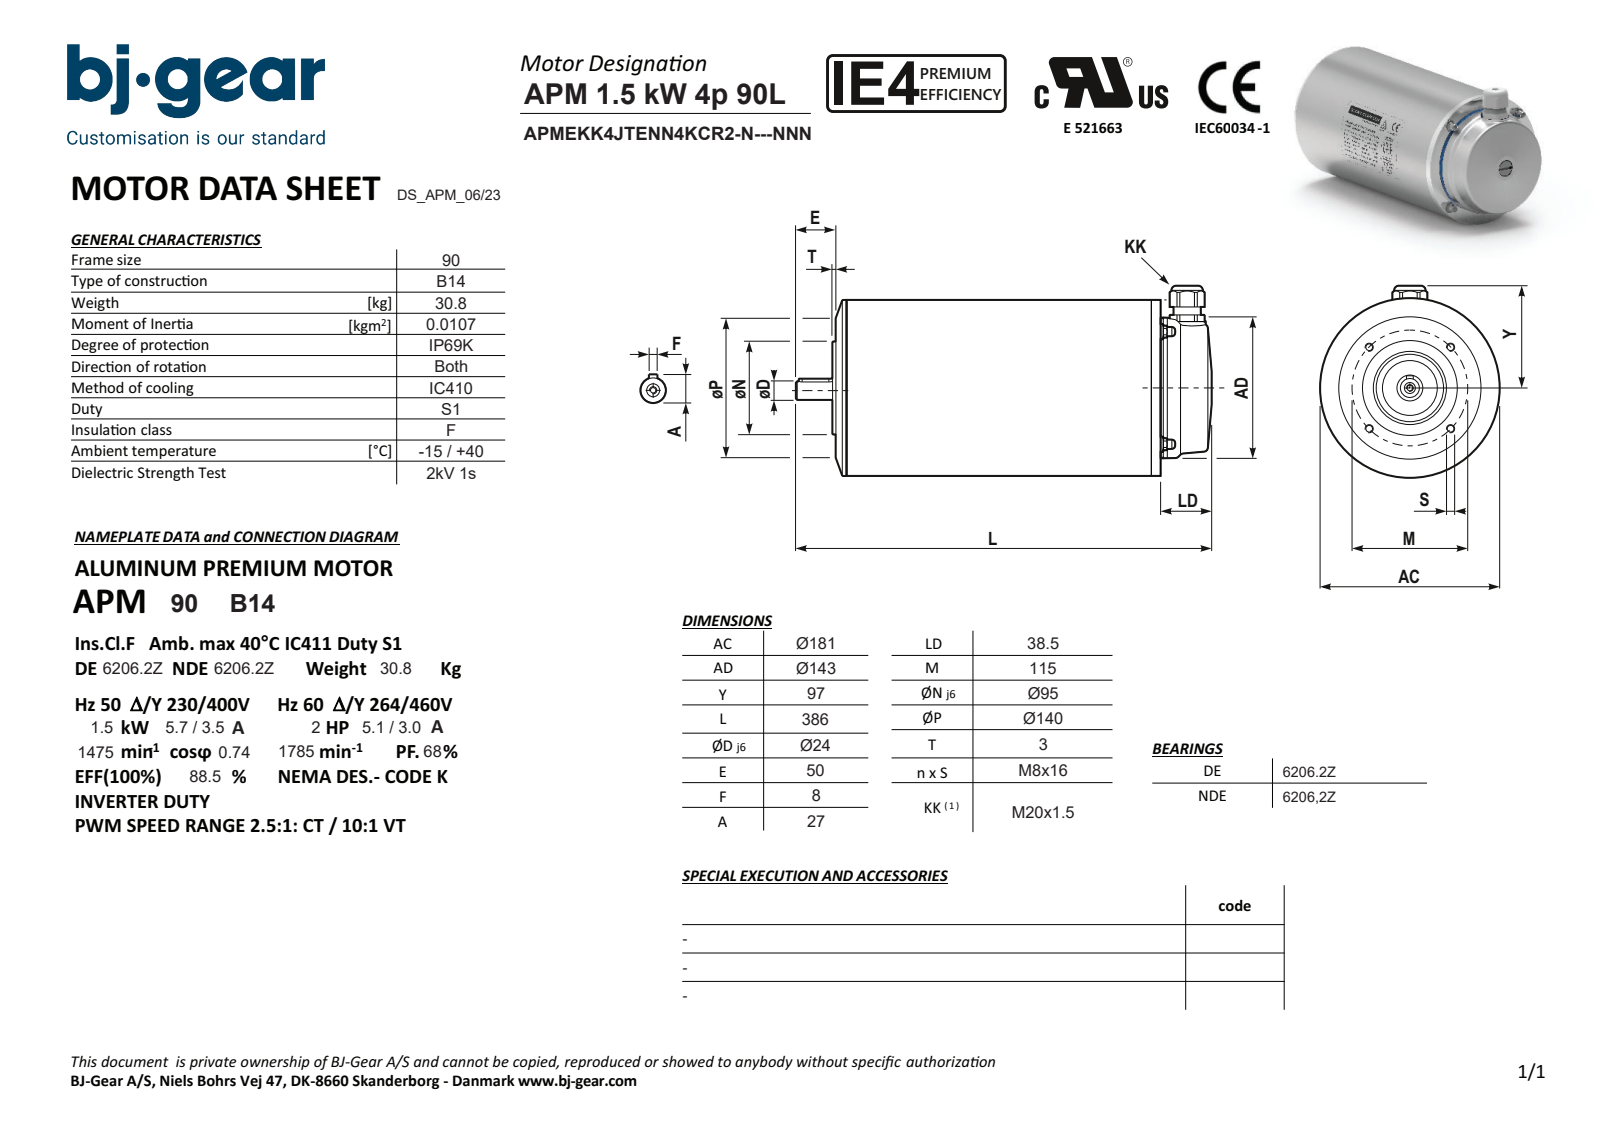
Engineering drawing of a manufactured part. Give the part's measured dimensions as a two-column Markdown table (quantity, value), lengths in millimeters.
| quantity | value |
| --- | --- |
| part name | APMEKK4JTENN4KCR2-N---NNN |
| STEP written by | Solid Edge (AUTOMOTIVE_DESIGN) |
| units | millimeters |
| bodies | 1 solid, 156 faces (75 planar, 50 cylindrical, 31 other) |
| overall size | 386 × 187.3 × 182.6 |
| volume | 8 327 000 mm³ |
| surface area | 247 972 mm² |
| round holes (diameter × count) | 6.65 × 5, 8.4 × 1, 16 × 1, 28 × 1, 82 × 1 |
| round bosses / shafts (diameter × count) | 11.5 × 4, 7 × 4, 182.6 × 1, 182.6 × 1, 143 × 1, 95 × 1, 30 × 1, 24 × 1 |
| partial cylindrical surfaces (radius × count) | 4 × 2, 13.2 × 1 |
| main face-to-face distances | 297.5, 6, 291.5, 3, 9, 300.5, 8, 336, 38.5, 330 |
| hole center spacings | 57.5, 81.32, 115 |
